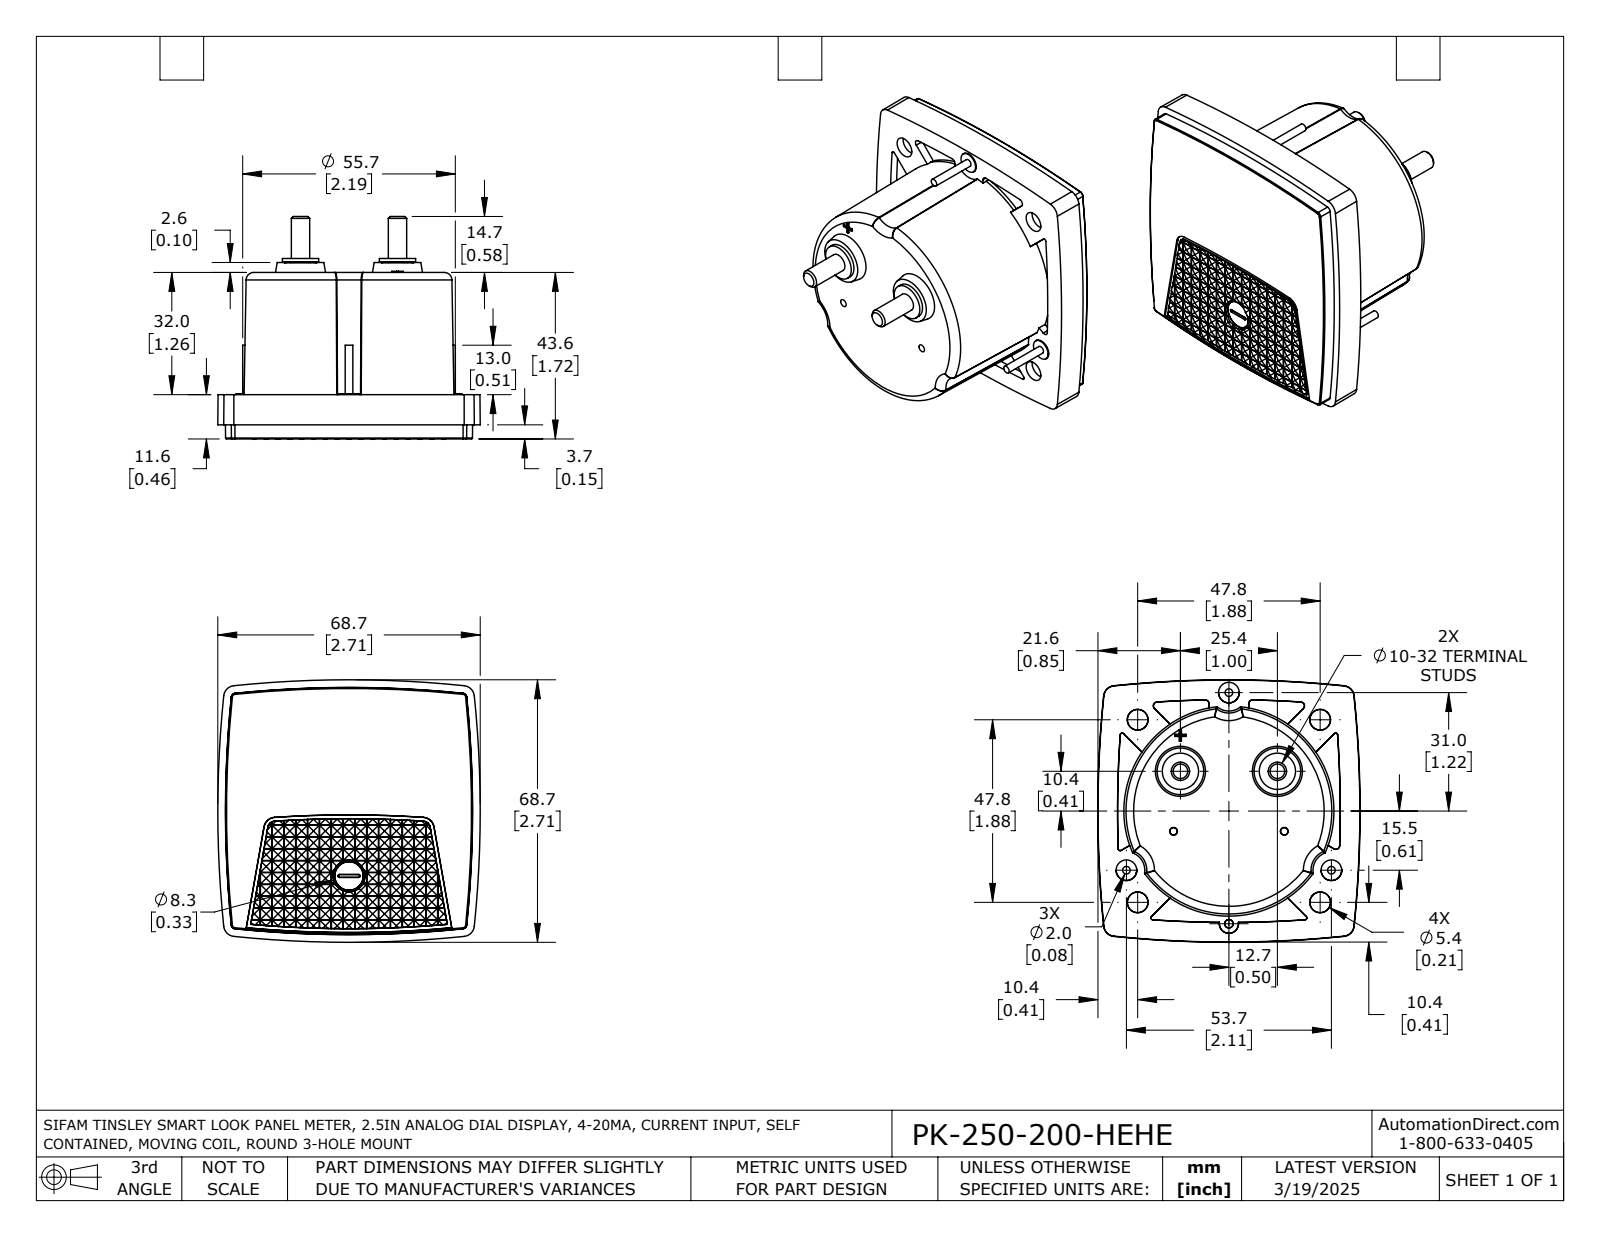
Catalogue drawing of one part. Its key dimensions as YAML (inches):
part_name: "PK-250-200-HEHE"
step_written_by: "SolidWorks 2021 (AUTOMOTIVE_DESIGN)"
units: inches
bodies: {solids: 1, faces: 1550, planar: 1165, cylindrical: 265, other: 120}
overall_size: [2.706, 2.706, 2.297]
volume: 7.594
surface_area: 30.41
round_bosses_or_shafts:
  - {diameter: 0.213, count: 3}
  - {diameter: 0.079, count: 3}
  - {diameter: 0.374, count: 2}
  - {diameter: 0.189, count: 2}
  - {diameter: 0.215, count: 1}
partial_cylinders:
  - {radius: 0.167, count: 2}
  - {radius: 1.083, count: 1}
face_to_face_distances: [1.717, 1.26, 0.457, 0.024, 0.087, 0.096, 0.311, 0.12, 0.072, 1.346]
